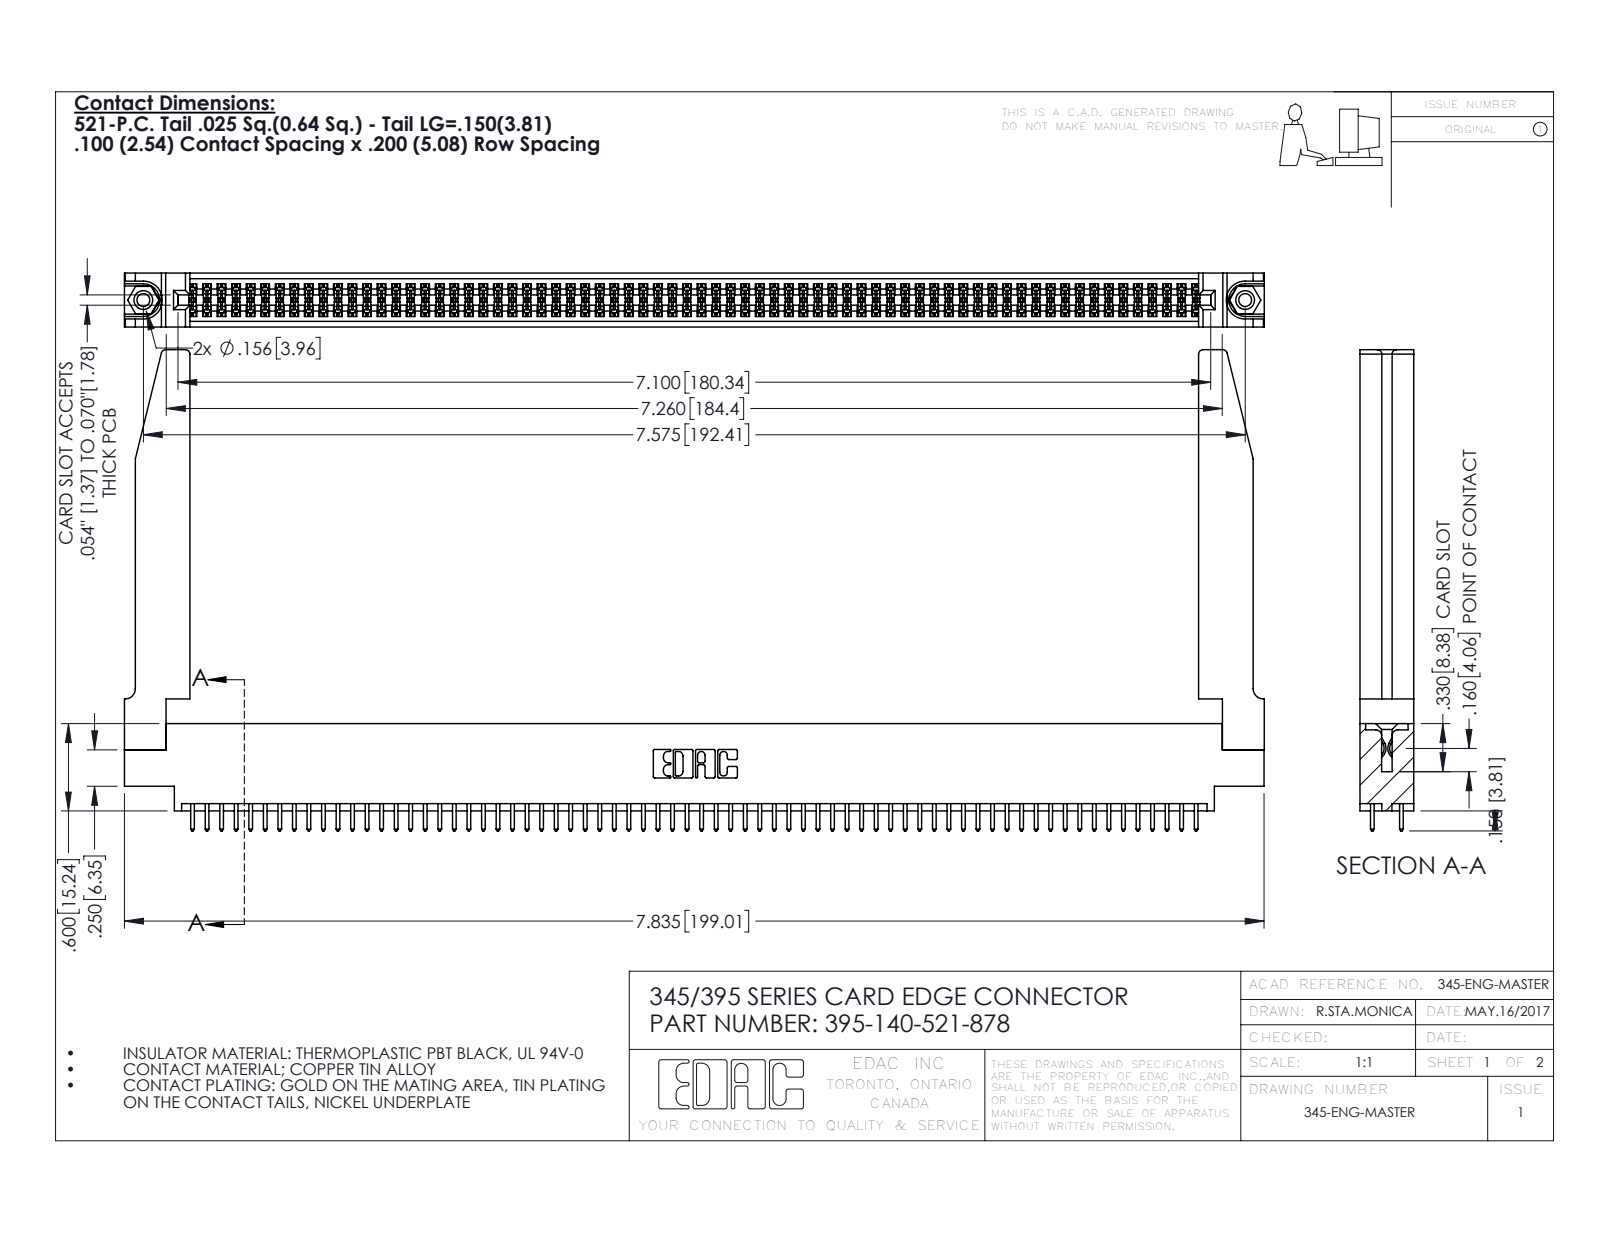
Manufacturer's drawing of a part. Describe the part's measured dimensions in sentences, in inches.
The part is named "345-220-078_345-220-078; 345-250-001_345-250-001-102; 345-292-001_345-293-121; 345 Part_0.170 Offset - 0.156 Dia-TH (+1 more)". Its 3-D file was written by "SolidWorks 2016 (CONFIG_CONTROL_DESIGN)". It is 145 solids with 7364 faces: 4846 planar, 2466 cylindrical and 52 other. Overall it measures 7.836 by 3.307 by 0.37 inches. Its volume is 1.659 cubic inches and its surface area 55.59 square inches. Round holes: 2 of diameter 0.089, 2 of diameter 0.125, 2 of diameter 0.156, 1 of diameter 0.064. Round bosses or shafts: 2 of diameter 0.155. Partial cylindrical surfaces (rounded edges, fillets, slot ends): 210 of radius 0.006, 140 of radius 0.01, 22 of radius 0.01, 8 of radius 0.03, 6 of radius 0.007, 6 of radius 0.031, 3 of radius 0.026, 2 of radius 0.014. The main face-to-face distances are 0.072, 0.298, 0.37, 0.098, 0.272, 0.025, 0.2, 0.225, 0.175, 0.149. The hole center spacings are 0.27, 7.339, 7.575.
